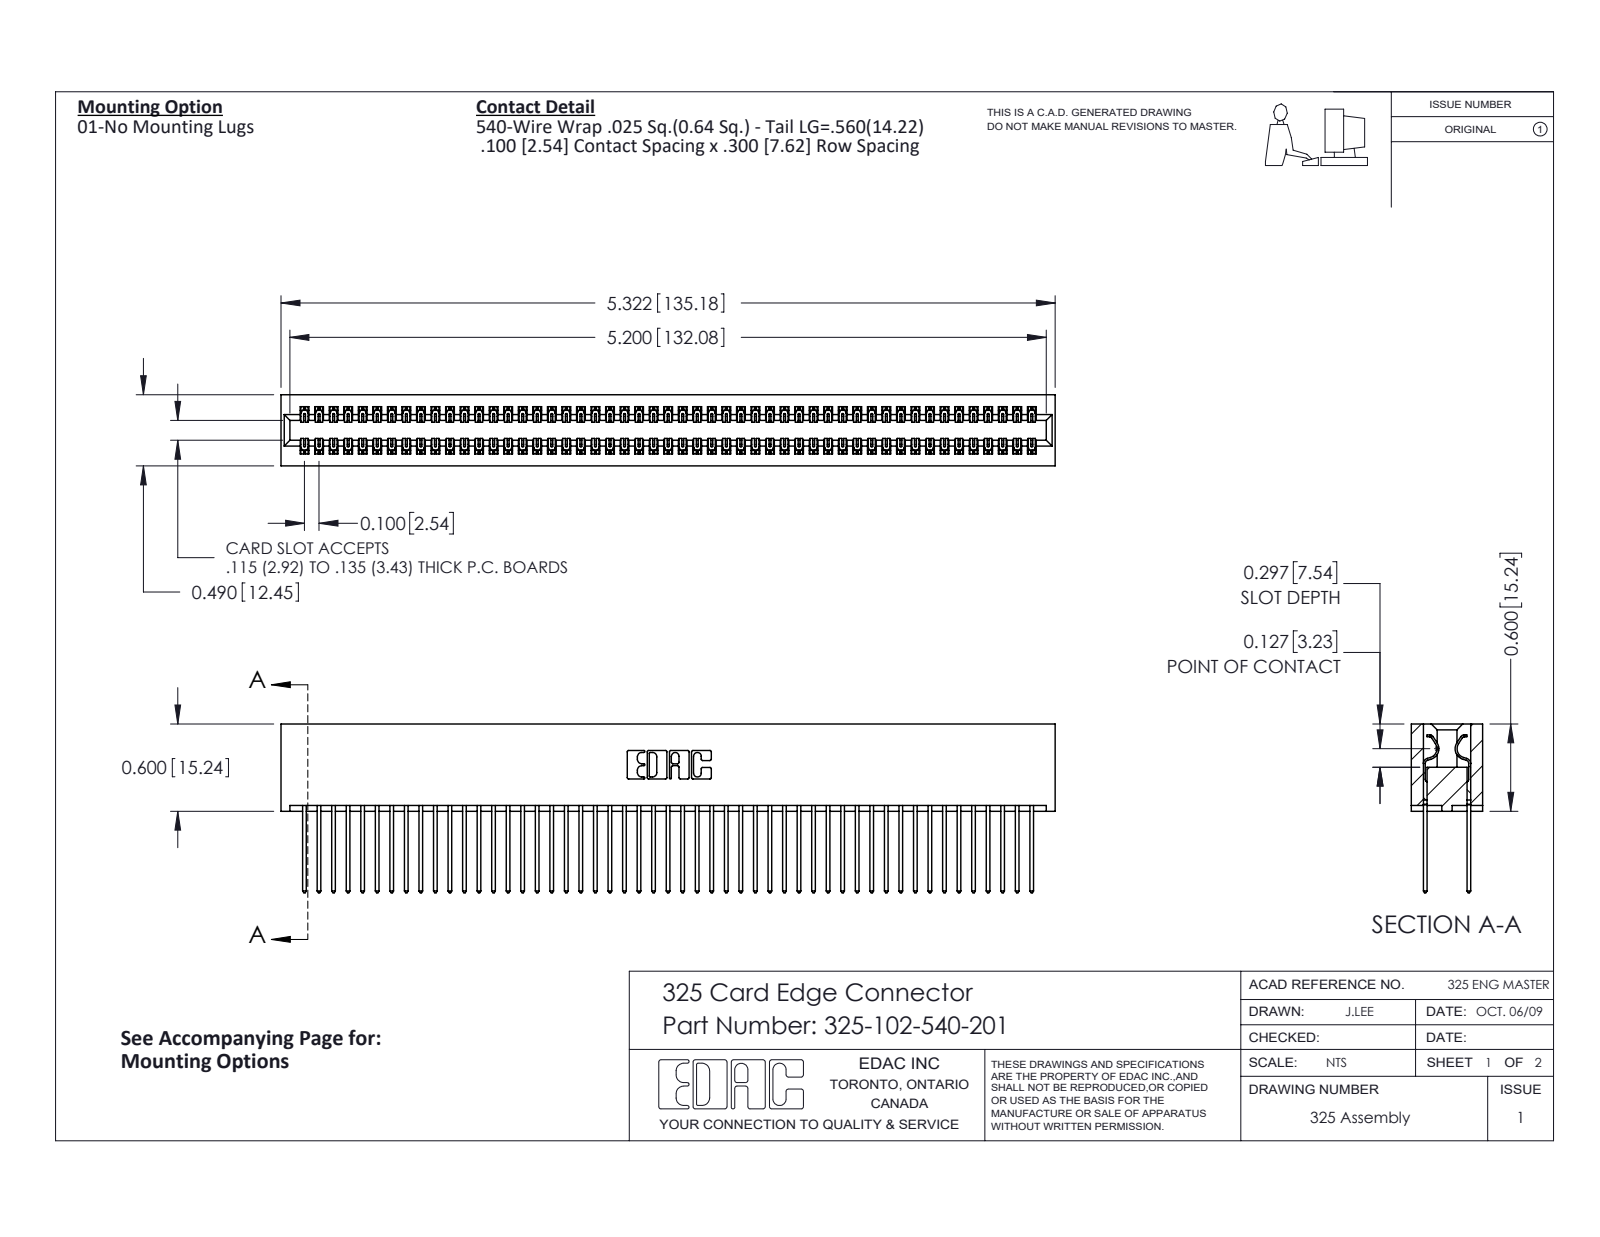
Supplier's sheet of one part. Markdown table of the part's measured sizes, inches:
| quantity | value |
| --- | --- |
| part name | 325-292-001_325-293-140; 325-102-540-201; 325 Part_Lugless |
| STEP written by | SolidWorks 2016 (CONFIG_CONTROL_DESIGN) |
| units | inches |
| bodies | 103 solids, 5410 faces (3738 planar, 1672 cylindrical, 0 other) |
| overall size | 5.322 × 1.16 × 0.49 |
| volume | 1.13 in³ |
| surface area | 38.96 in² |
| partial cylindrical surfaces (radius × count) | 0.006 × 153, 0.01 × 102, 0.01 × 22, 0.007 × 6, 0.031 × 6, 0.026 × 3, 0.014 × 2, 0.022 × 2 |
| main face-to-face distances | 0.083, 0.407, 0.3, 0.107, 0.383, 0.025, 0.325, 0.49, 0.275, 0.56 |
